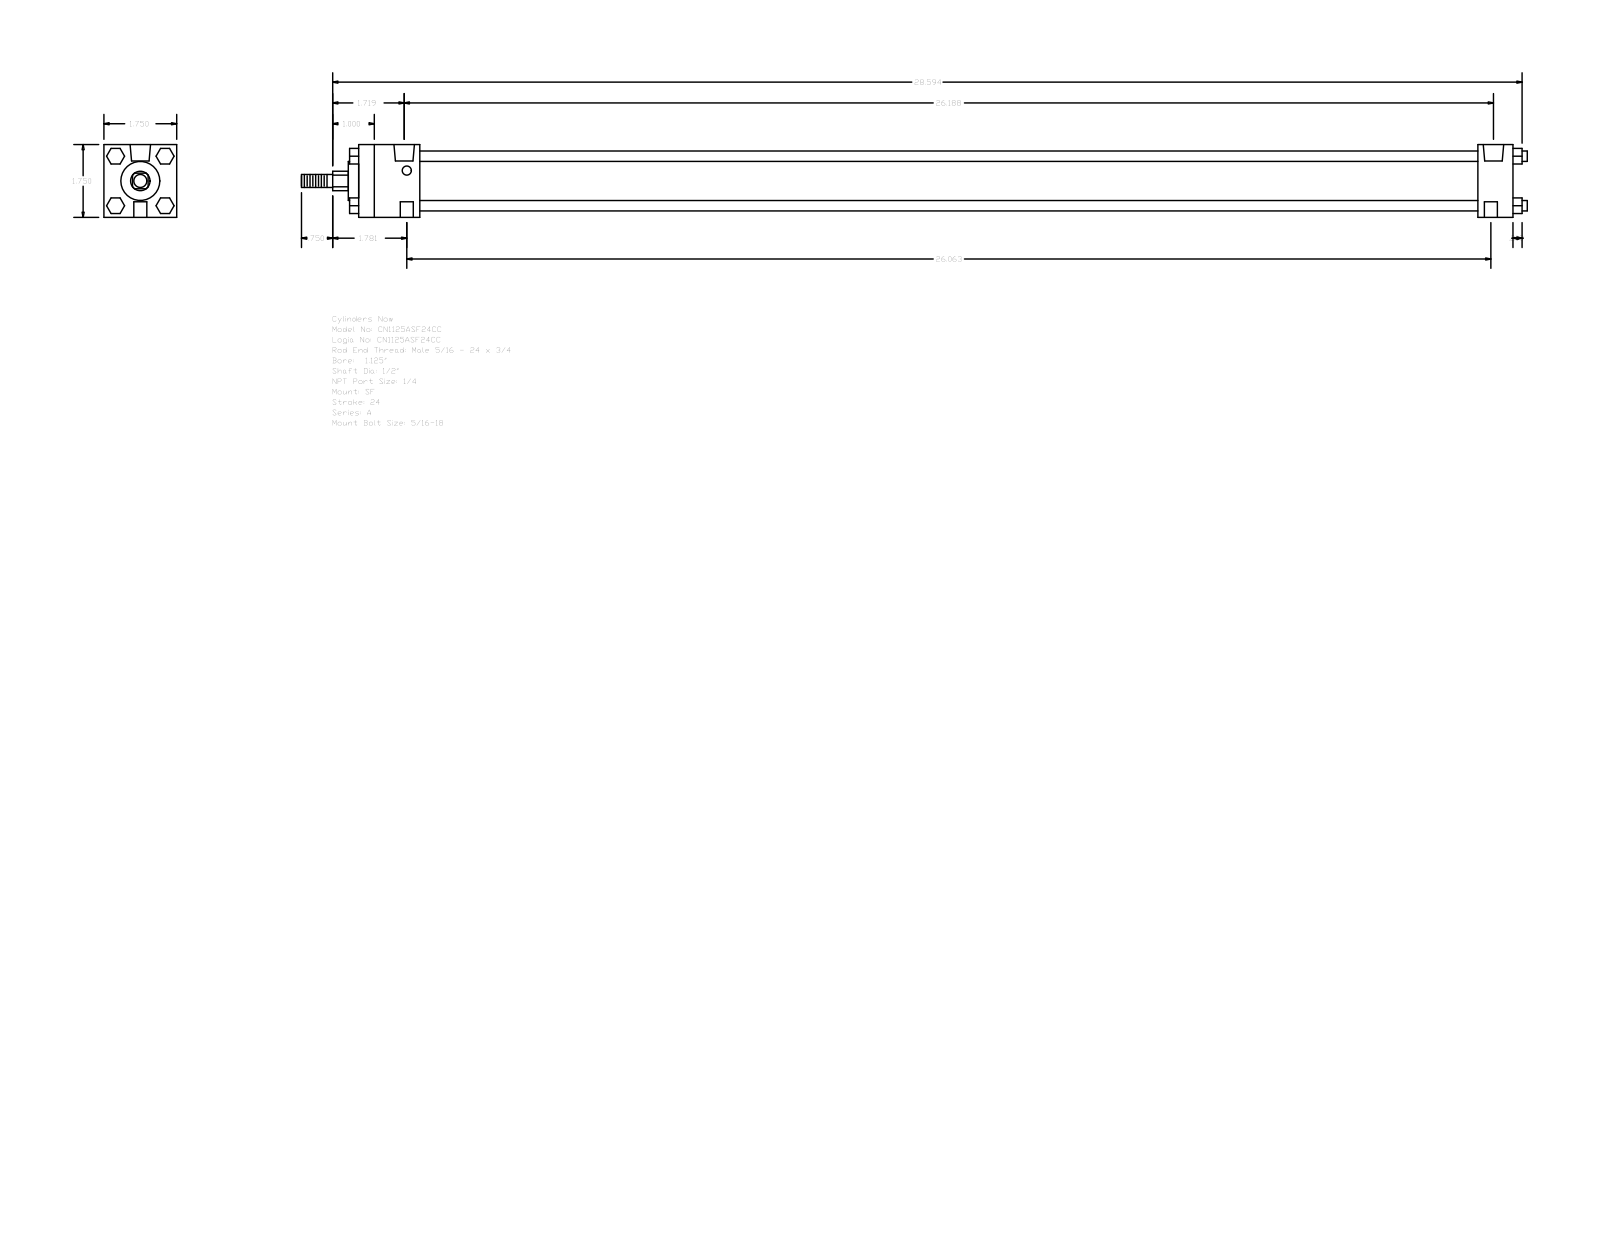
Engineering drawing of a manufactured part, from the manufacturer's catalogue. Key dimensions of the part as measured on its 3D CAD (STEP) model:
Part name (STEP PRODUCT): A_SF__0112_0.5
STEP written by: GSSL Pune (CONFIG_CONTROL_DESIGN)
Units: millimetres
Bodies: 0 solids, 120 faces (92 planar, 28 cylindrical, 0 other)
Overall size (bounding box): 748.51 × 44.45 × 44.45
Round holes (diameter × count): ⌀5.56 ×2, ⌀7.94 ×2, ⌀12.49 ×2
Round bosses / shafts (diameter × count): ⌀6.35 ×4, ⌀31.88 ×1, ⌀23.81 ×1, ⌀12.7 ×1, ⌀7.94 ×1
Partial cylindrical surfaces — rounded edges, fillets, slot ends (radius × count): R5.94 ×1
Main face-to-face distances: 44.46, 704.85, 683.41, 21.44, 37.3, 646.11, 667.55, 9.53, 5.59, 26.99
Hole centre spacings: 661.99, 1.58, 1.59, 663.57, 663.58, 665.16
